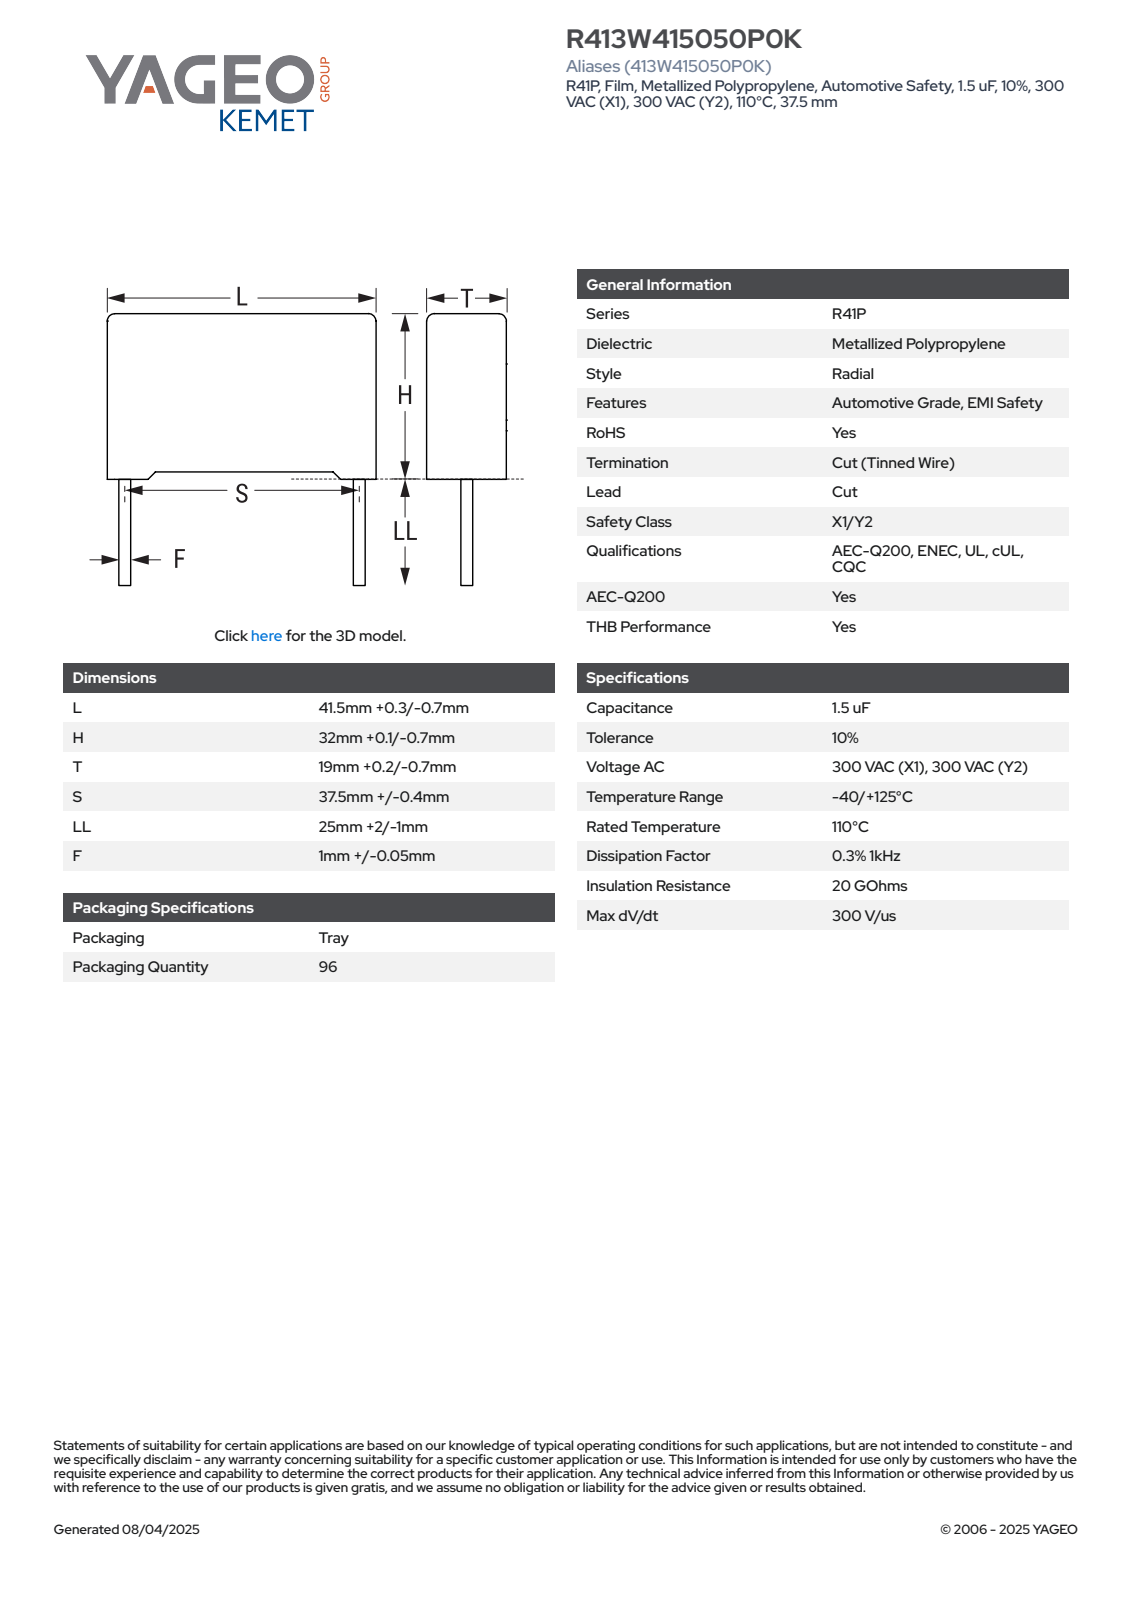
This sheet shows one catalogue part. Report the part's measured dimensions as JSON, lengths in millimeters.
{"part_name": "CFR_RB2_41.5X32X19_L41.8H32.1T19.2S37.5LL27F1.05", "step_written_by": "SolidWorks 2021 (AUTOMOTIVE_DESIGN)", "units": "millimeters", "bodies": {"solids": 4, "faces": 85, "planar": 77, "cylindrical": 8, "other": 0}, "overall_size": [59.1, 41.8, 19.2], "volume_mm3": 25030, "surface_area_mm2": 5775, "round_bosses_or_shafts": [[1.05, 2]], "partial_cylinders_radius": [[0.5, 4]], "face_to_face_distances": [19.2, 30.99, 41.8, 0.36, 31.35, 0.75, 1.11, 32.1, 1.39, 40.41]}
